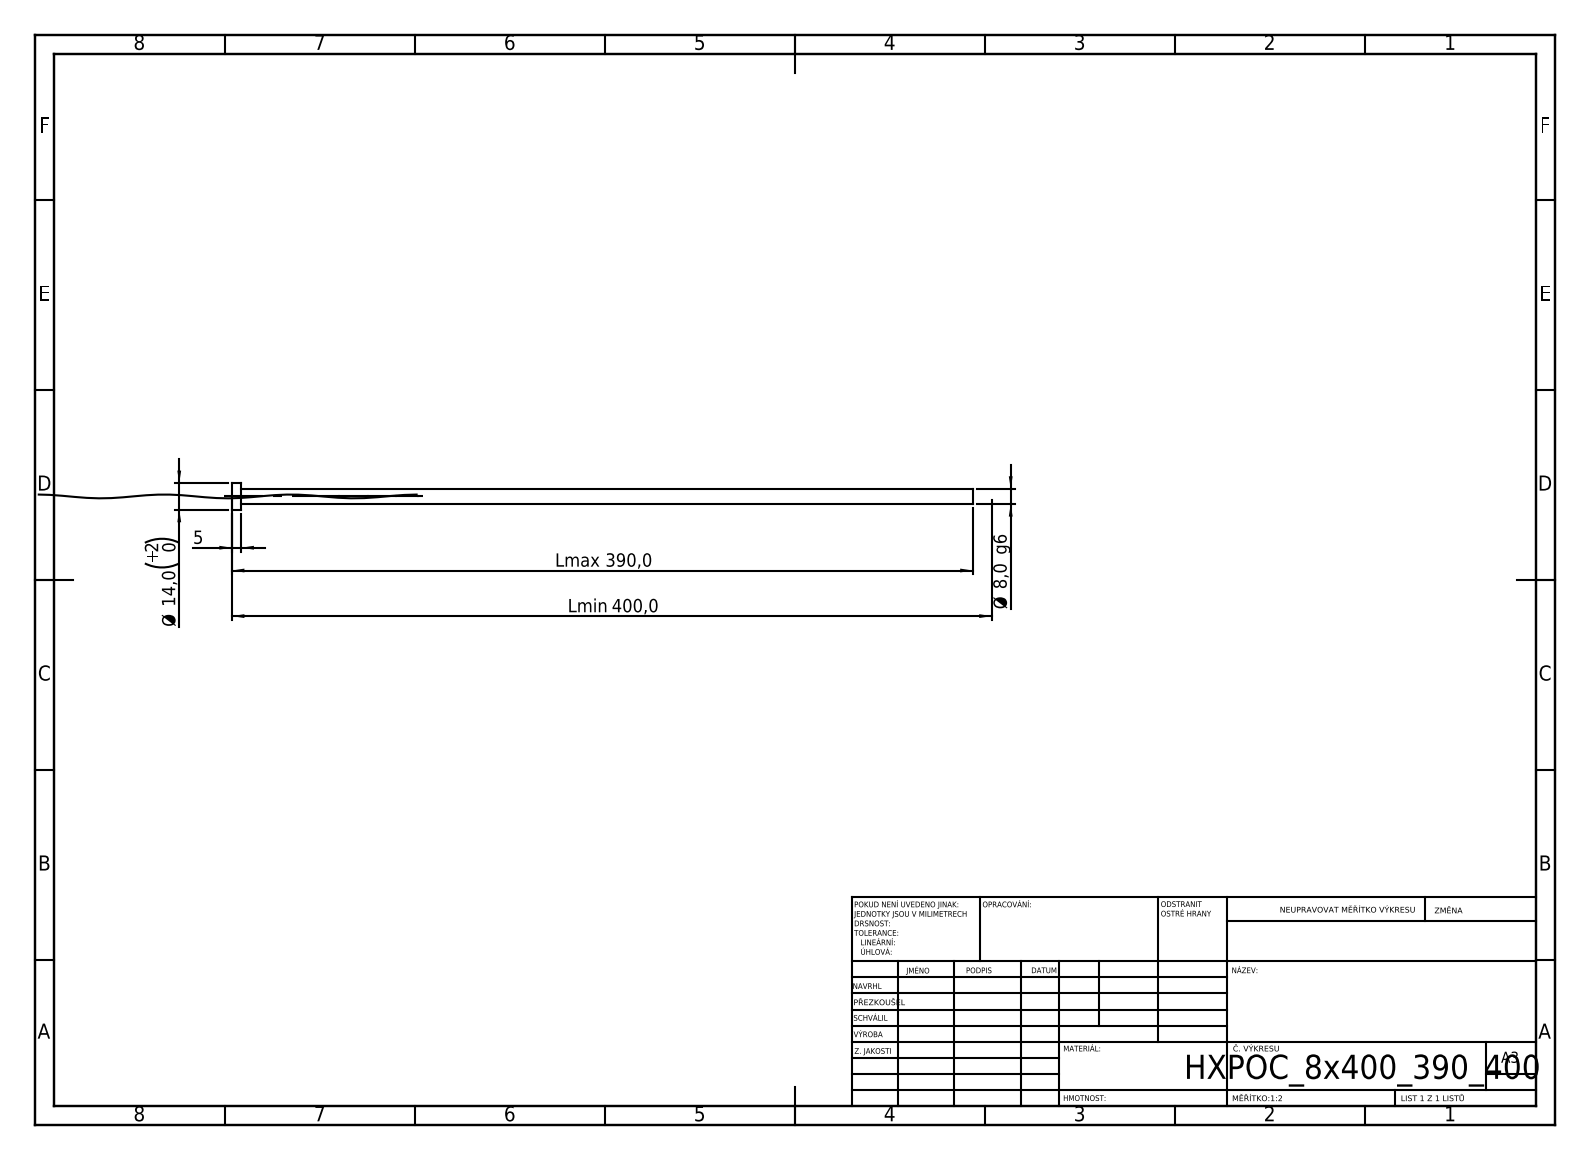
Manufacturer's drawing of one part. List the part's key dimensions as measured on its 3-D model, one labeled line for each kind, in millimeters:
STEP written by: SolidWorks 2019 (CONFIG_CONTROL_DESIGN)
Units: millimetres
Bodies: 1 solid, 10 faces (4 planar, 4 cylindrical, 2 other)
Overall size (bounding box): 390 × 14 × 14
Volume: 20 120 mm³ · Surface area: 10 254 mm²
Round bosses / shafts (diameter × count): ⌀14 ×1, ⌀8 ×1
Main face-to-face distances: 5, 390, 385, 97.8, 92.8, 292.2
